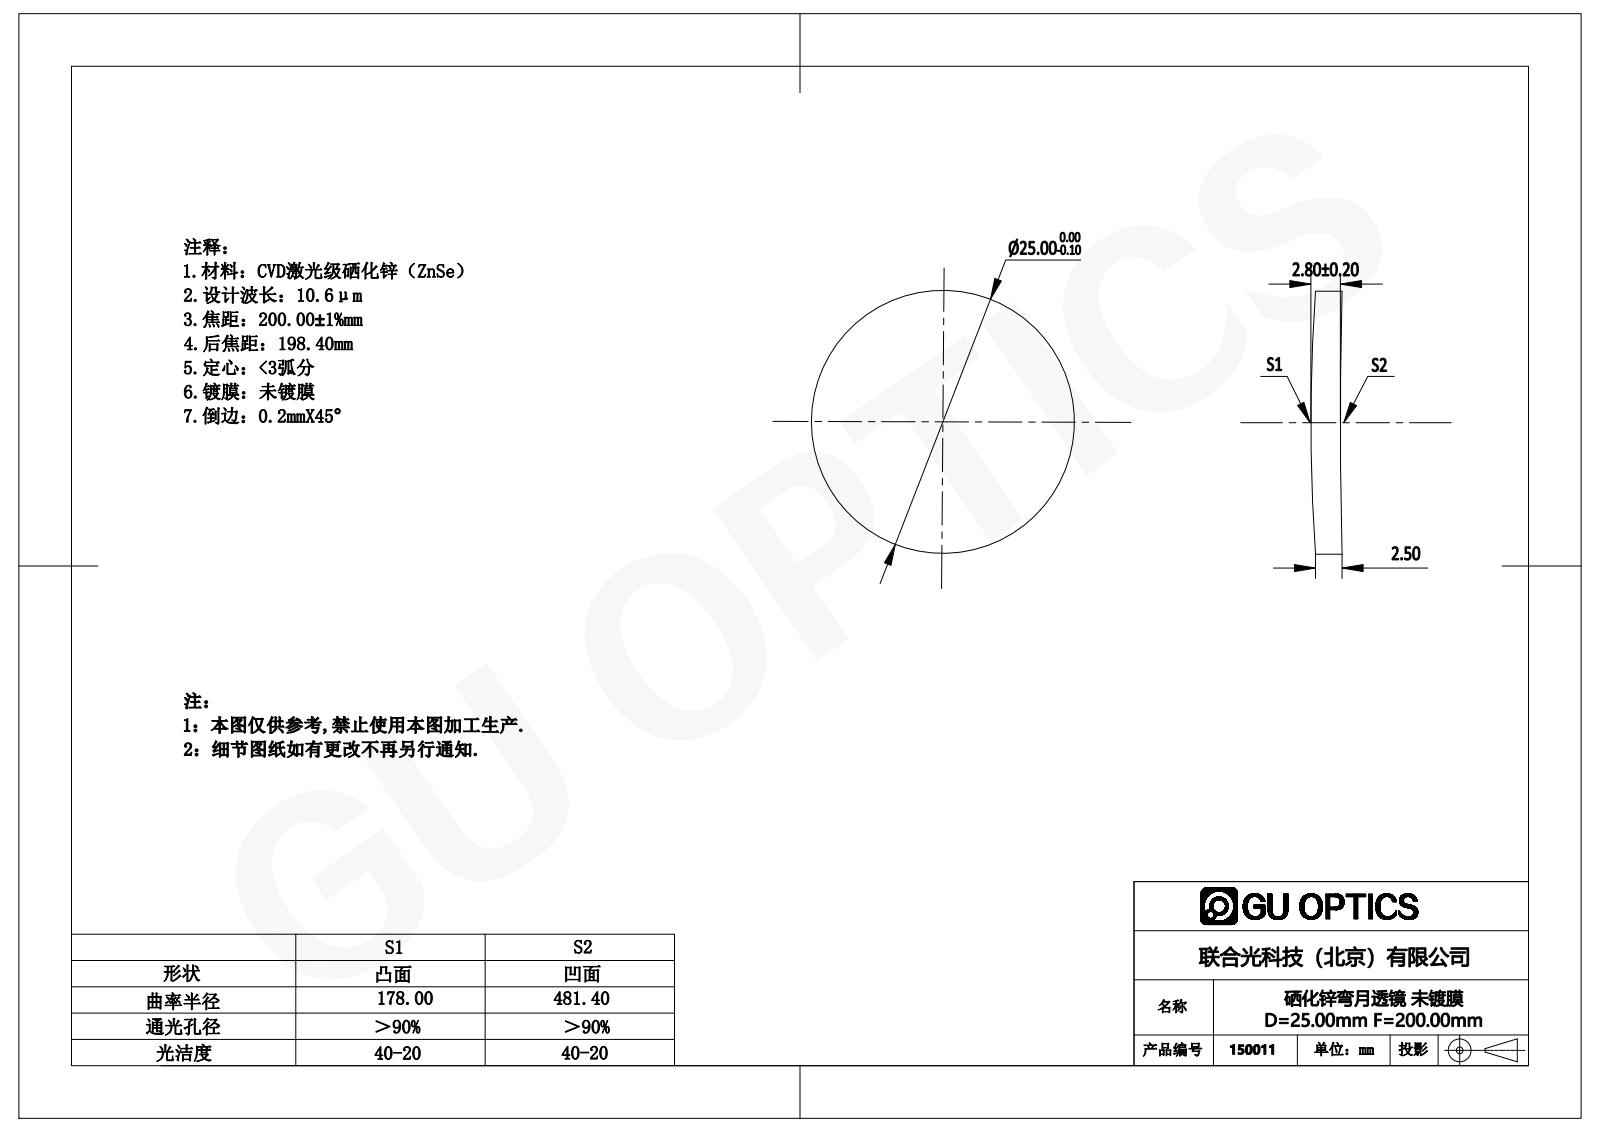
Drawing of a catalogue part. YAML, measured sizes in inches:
part_name: "150011"
step_written_by: "SolidWorks 2016 (AUTOMOTIVE_DESIGN)"
units: inches
bodies: {solids: 1, faces: 6, planar: 0, cylindrical: 2, other: 4}
overall_size: [0.984, 0.984, 0.117]
volume: 0.08
surface_area: 1.831
round_bosses_or_shafts:
  - {diameter: 0.984, count: 1}
